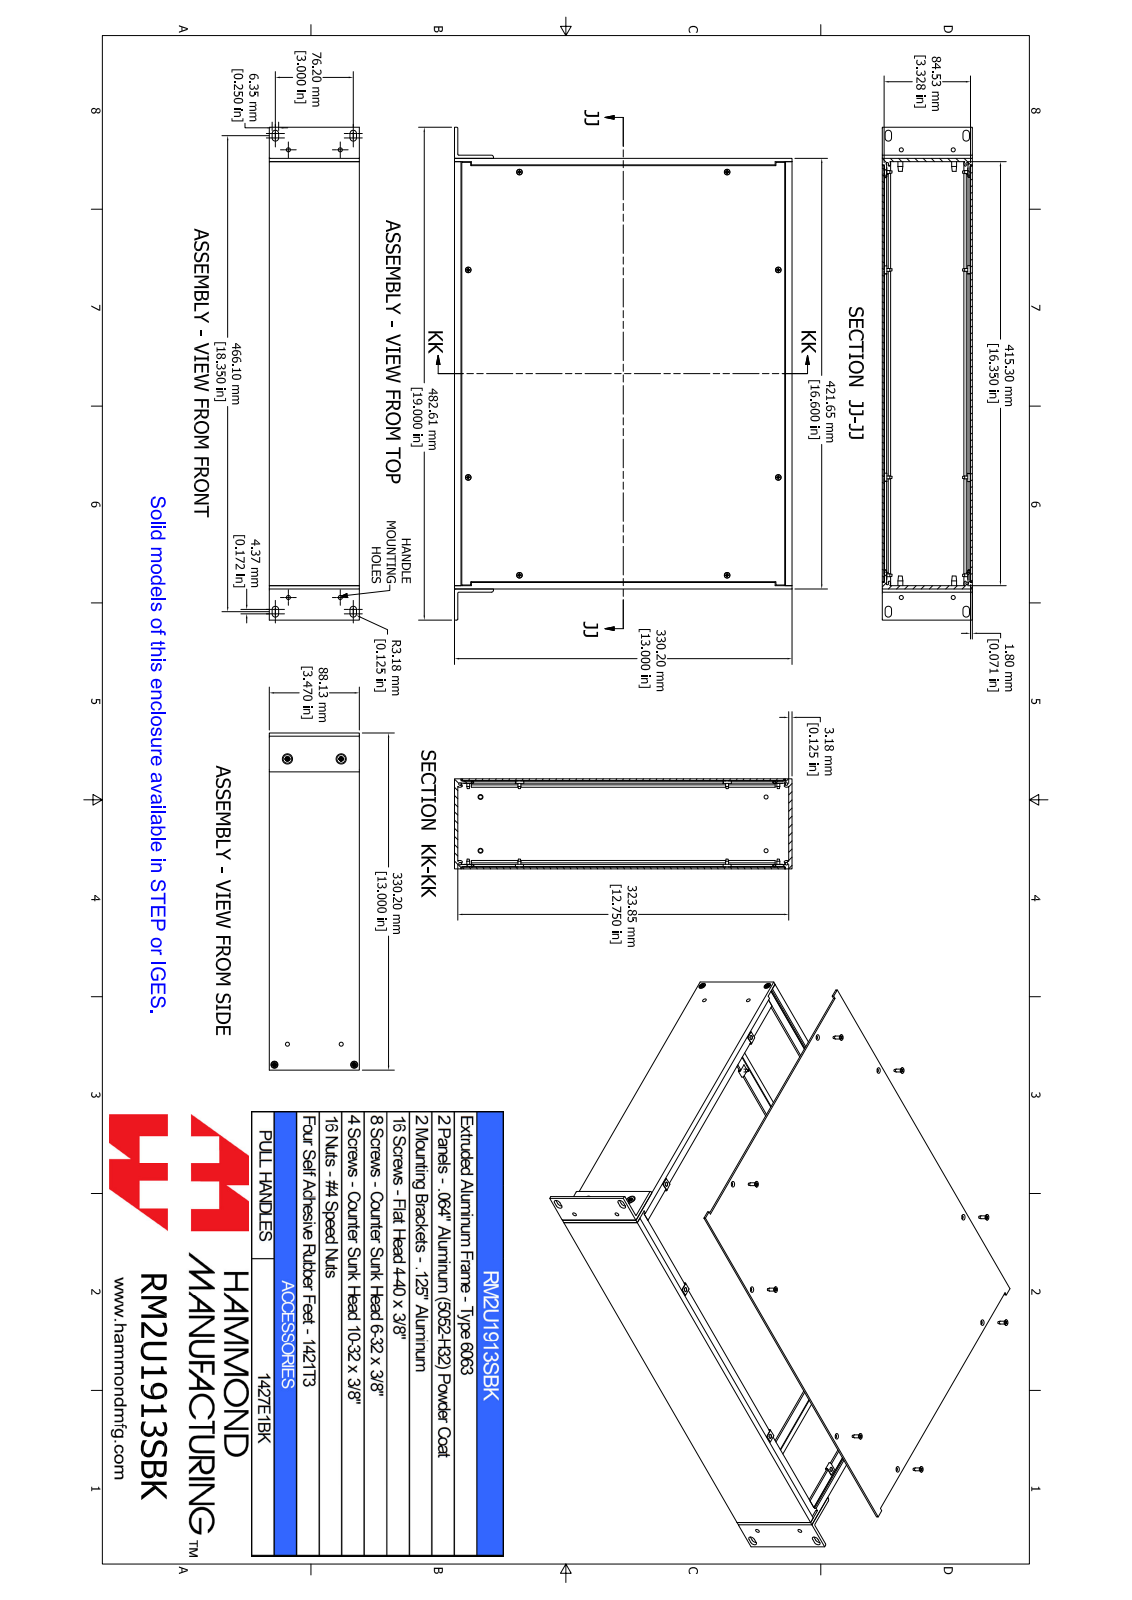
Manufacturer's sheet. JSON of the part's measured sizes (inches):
{"part_name": "RM2U1913SBK", "step_written_by": "SolidWorks 2021 (AUTOMOTIVE_DESIGN)", "units": "inches", "bodies": {"solids": 52, "faces": 1352, "planar": 636, "cylindrical": 220, "other": 496}, "overall_size": [19, 13, 3.47], "volume_in3": 63.71, "surface_area_in2": 1437, "round_holes": [[0.098, 8], [0.118, 8], [0.157, 8], [0.169, 8], [0.138, 4], [0.156, 4], [0.157, 4], [0.197, 2]], "round_bosses_or_shafts": [[0.214, 8], [0.112, 8], [0.238, 4], [0.138, 4], [0.333, 2], [0.19, 2]], "partial_cylinders_radius": [[0.039, 20], [0.125, 16], [0.049, 14], [0.05, 8], [0.037, 6], [0.038, 4], [0.079, 2]], "face_to_face_distances": [0.071, 3.399, 3.47, 3.328, 0.125, 0.125, 16.6, 13, 12.75, 12.875], "hole_center_spacings": [8, 10.662, 11.801, 12.067, 0.935, 0.936, 2, 2.071]}
